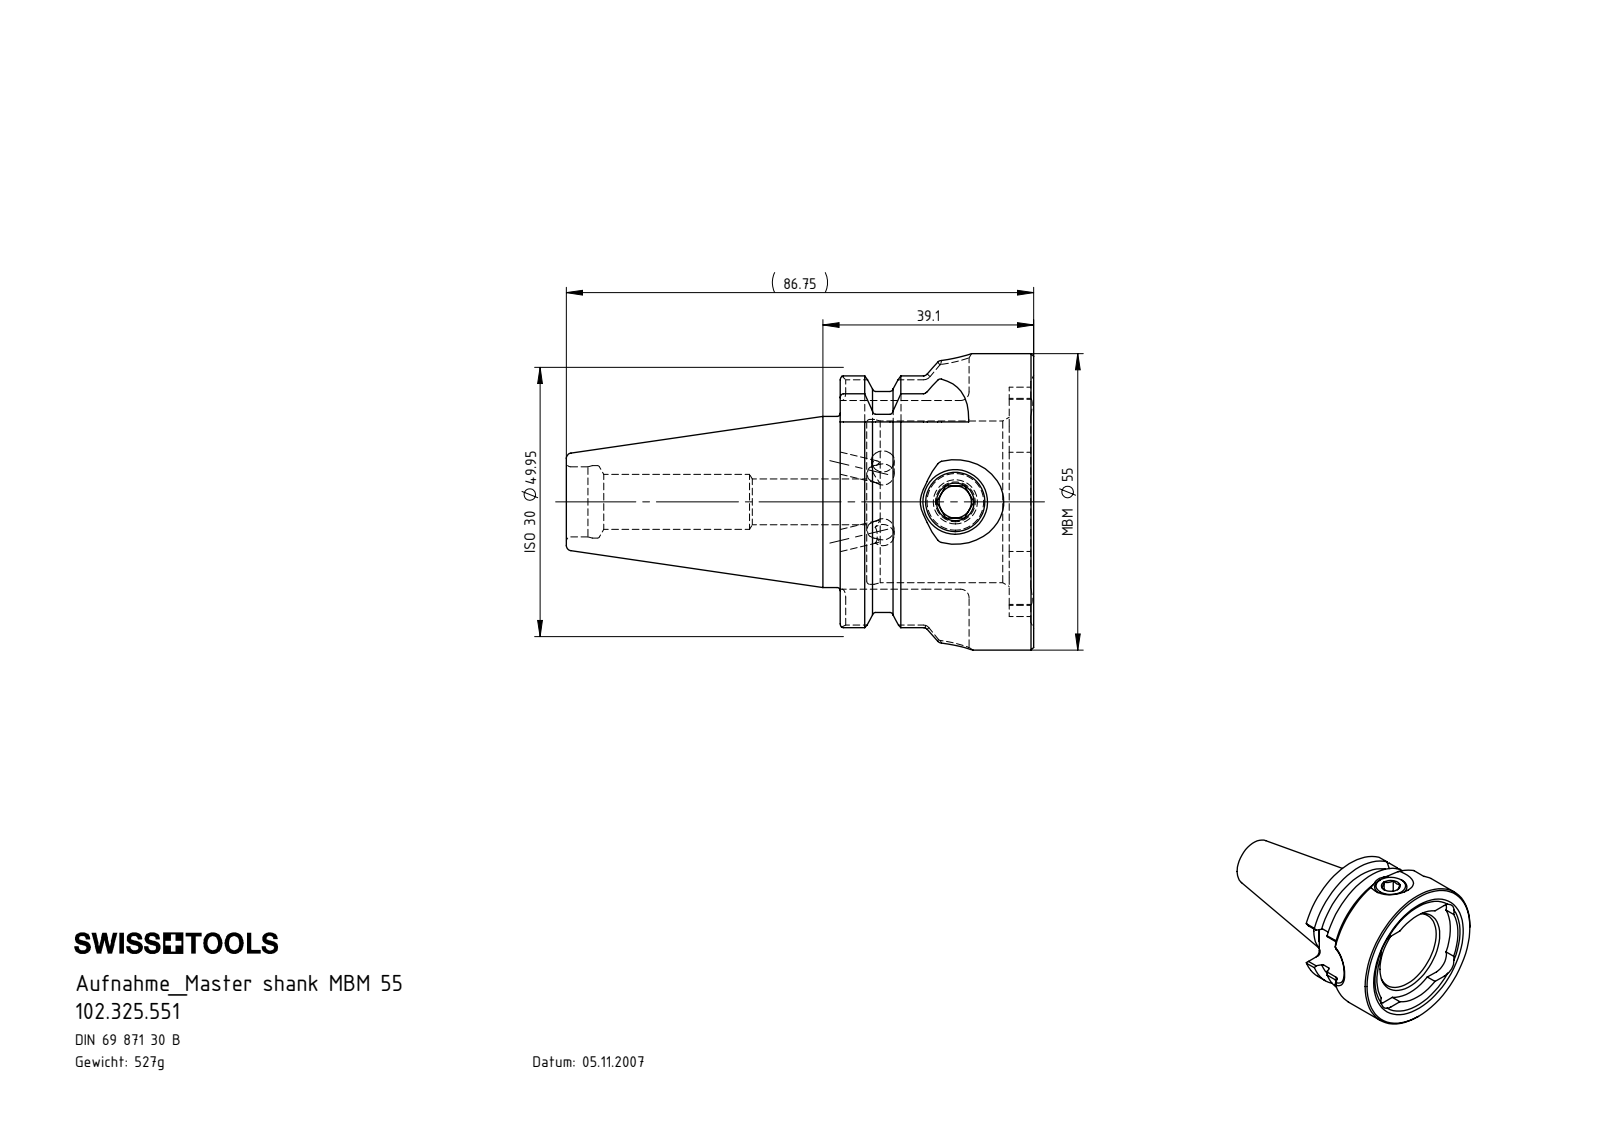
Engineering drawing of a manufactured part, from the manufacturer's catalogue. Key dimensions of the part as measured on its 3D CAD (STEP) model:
Part name (STEP PRODUCT): 102.325.551; MB5-ER1.001.017_A; SB3-MB5.K01.039_C_mit Bundkhlung
STEP written by: SolidWorks 2017 (CONFIG_CONTROL_DESIGN)
Units: millimetres
Bodies: 2 solids, 212 faces (49 planar, 65 cylindrical, 98 other)
Overall size (bounding box): 86.75 × 55 × 55
Volume: 67 180 mm³ · Surface area: 20 445 mm²
Round holes (diameter × count): ⌀4 ×2, ⌀4.2 ×1, ⌀6 ×1, ⌀8.5 ×1, ⌀10.2 ×1, ⌀11 ×1, ⌀13 ×1, ⌀13.45 ×1, ⌀30 ×1, ⌀30.6 ×1
Round bosses / shafts (diameter × count): ⌀55 ×1, ⌀31.75 ×1, ⌀12 ×1
Partial cylindrical surfaces — rounded edges, fillets, slot ends (radius × count): R1.6 ×8, R5.2 ×4, R8 ×1, R8.05 ×1, R18.5 ×1, R21.27 ×1, R22.02 ×1, R24.98 ×1
Main face-to-face distances: 4.9, 35.9, 31, 31.35, 26.45, 4.55, 35, 35.35, 30.45, 4
